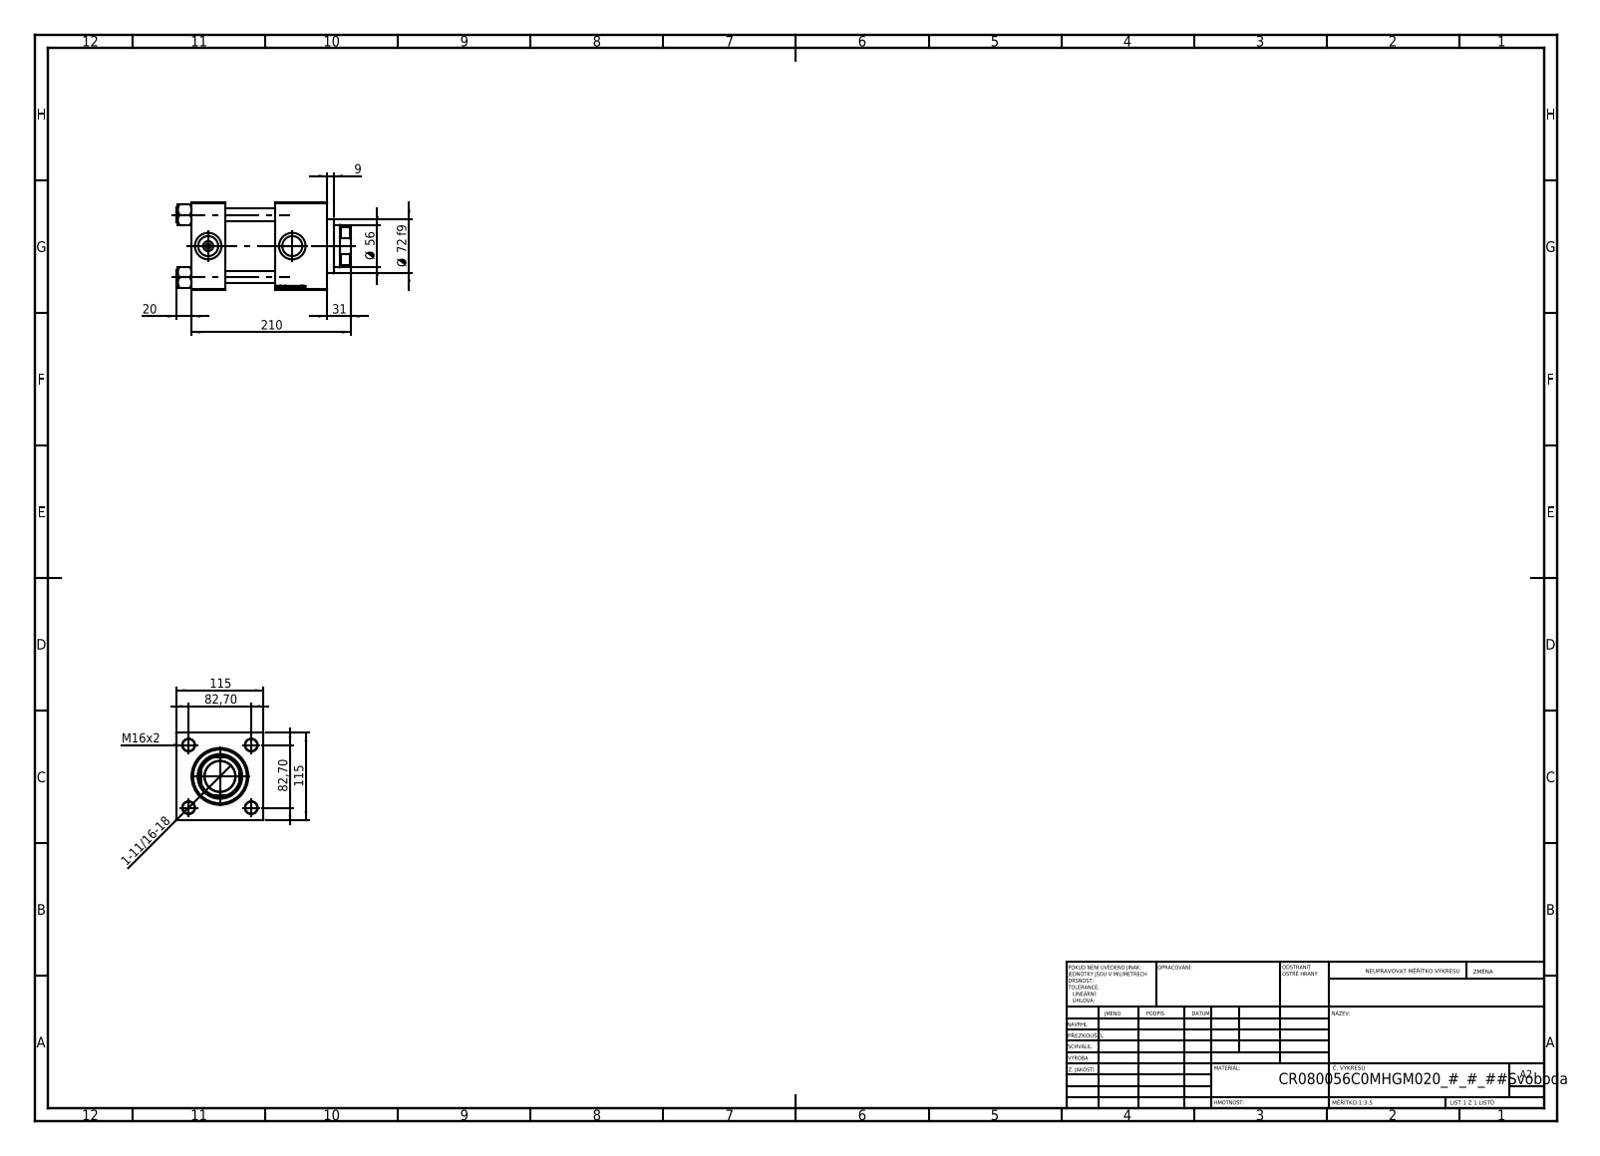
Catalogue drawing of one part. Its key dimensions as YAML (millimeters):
part_name: "V215_VC_A; NUT_M5_C; V215CR_C_Body; V215CR_C_TYCINKA (+1 more)"
step_written_by: "SolidWorks 2019 (CONFIG_CONTROL_DESIGN)"
units: millimeters
bodies: {solids: 11, faces: 1193, planar: 573, cylindrical: 84, other: 536}
overall_size: [230, 115, 115]
volume: 1862000
surface_area: 280215
round_holes:
  - {diameter: 16, count: 4}
  - {diameter: 7, count: 2}
  - {diameter: 26.44, count: 2}
  - {diameter: 35, count: 2}
  - {diameter: 40.5, count: 1}
  - {diameter: 56, count: 1}
  - {diameter: 59, count: 1}
  - {diameter: 61, count: 1}
  - {diameter: 72, count: 1}
  - {diameter: 80, count: 1}
round_bosses_or_shafts:
  - {diameter: 19, count: 4}
  - {diameter: 86, count: 1}
partial_cylinders:
  - {radius: 27, count: 1}
face_to_face_distances: [115, 44, 110, 66, 179, 135, 69, 20, 150.3, 106.3]
hole_center_spacings: [58.48, 82.7, 116.96, 111]
